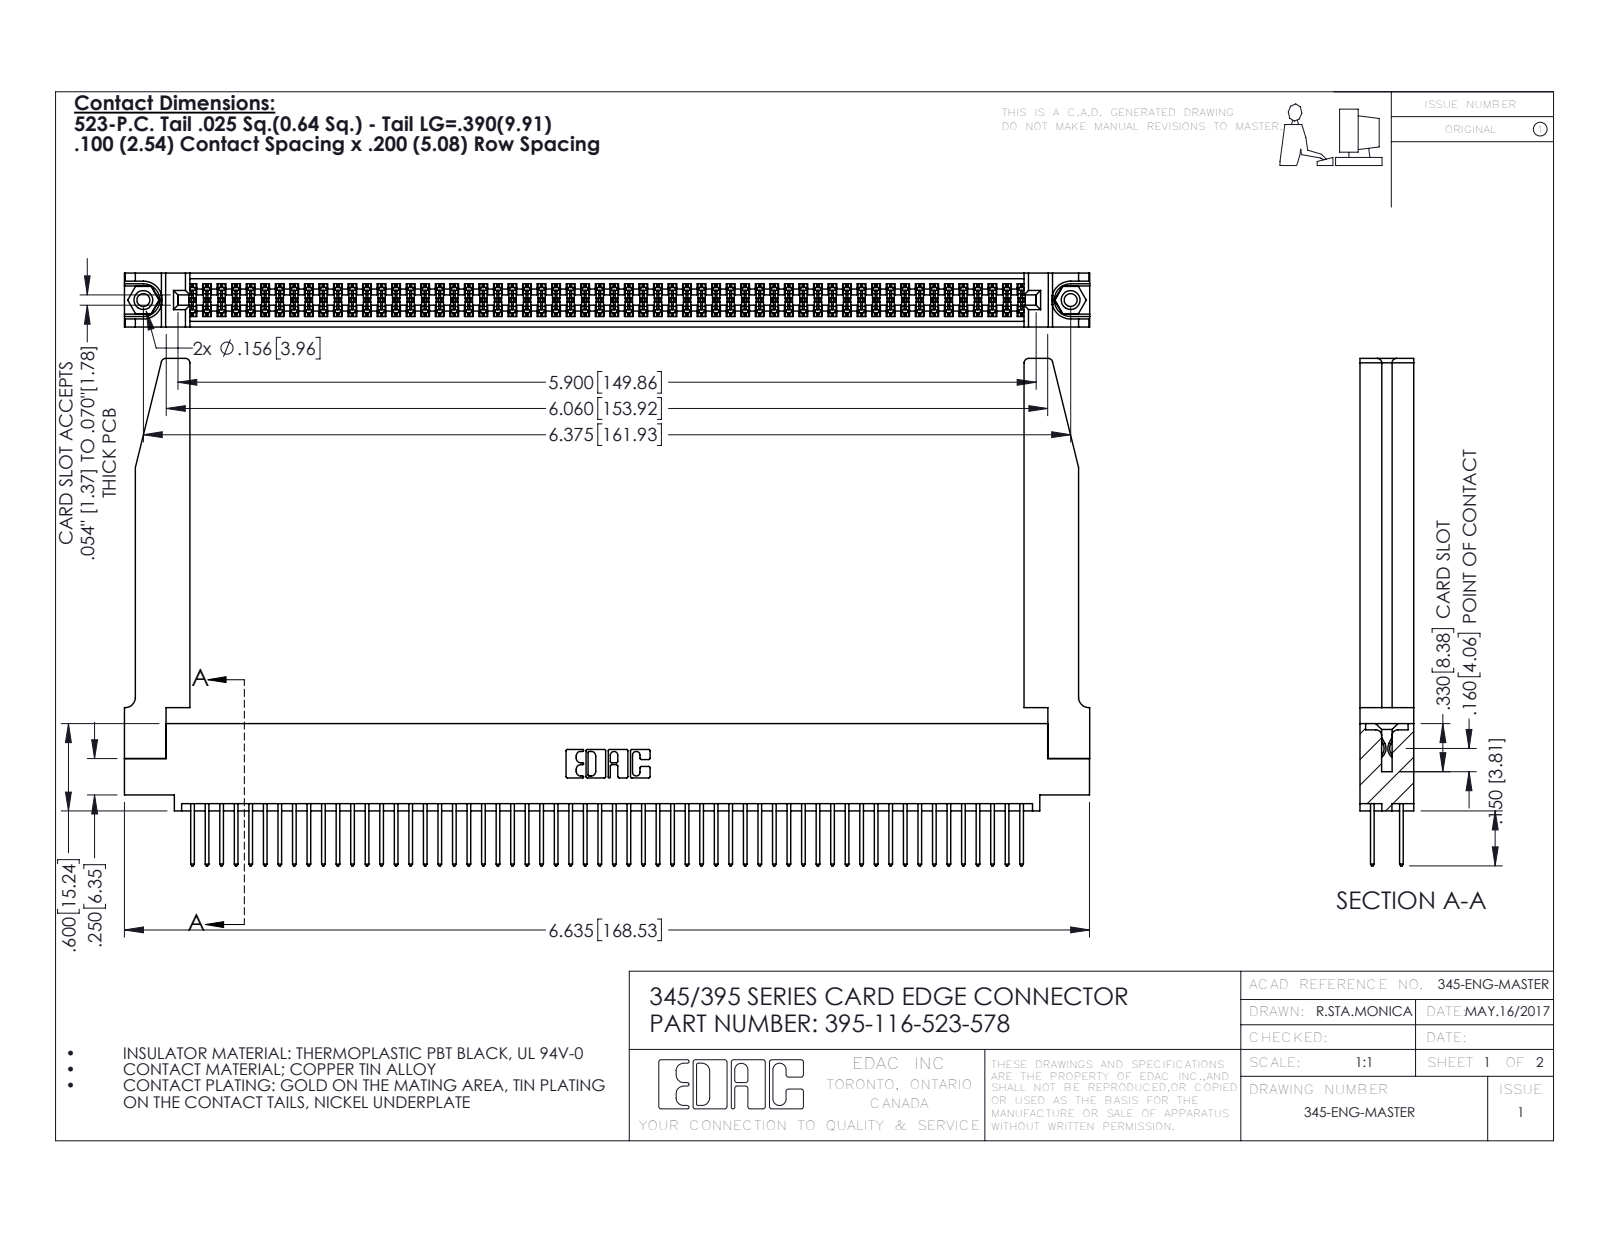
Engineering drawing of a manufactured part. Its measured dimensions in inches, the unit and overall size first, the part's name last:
Units: inches
Overall size (bounding box): 6.636 × 3.487 × 0.37
Round holes (diameter × count): ⌀0.089 ×2, ⌀0.125 ×2, ⌀0.156 ×2, ⌀0.064 ×1
Round bosses / shafts (diameter × count): ⌀0.155 ×2
Partial cylindrical surfaces — rounded edges, fillets, slot ends (radius × count): R0.006 ×174, R0.01 ×116, R0.01 ×22, R0.03 ×8, R0.007 ×6, R0.031 ×6, R0.026 ×3, R0.014 ×2
Main face-to-face distances: 0.072, 0.298, 0.37, 0.2, 0.098, 0.272, 0.025, 0.225, 0.175, 0.15
Hole centre spacings: 0.27, 6.139, 6.375
Volume: 1.492 in³ · Surface area: 51.11 in²
Bodies: 121 solids, 6164 faces (4054 planar, 2058 cylindrical, 52 other)
Part name (STEP PRODUCT): 345-292-001_345-293-123; 345-250-001_345-250-001-102; 395-116-523-578; 345-220-078_345-220-078 (+1 more)
STEP written by: SolidWorks 2016 (CONFIG_CONTROL_DESIGN)
